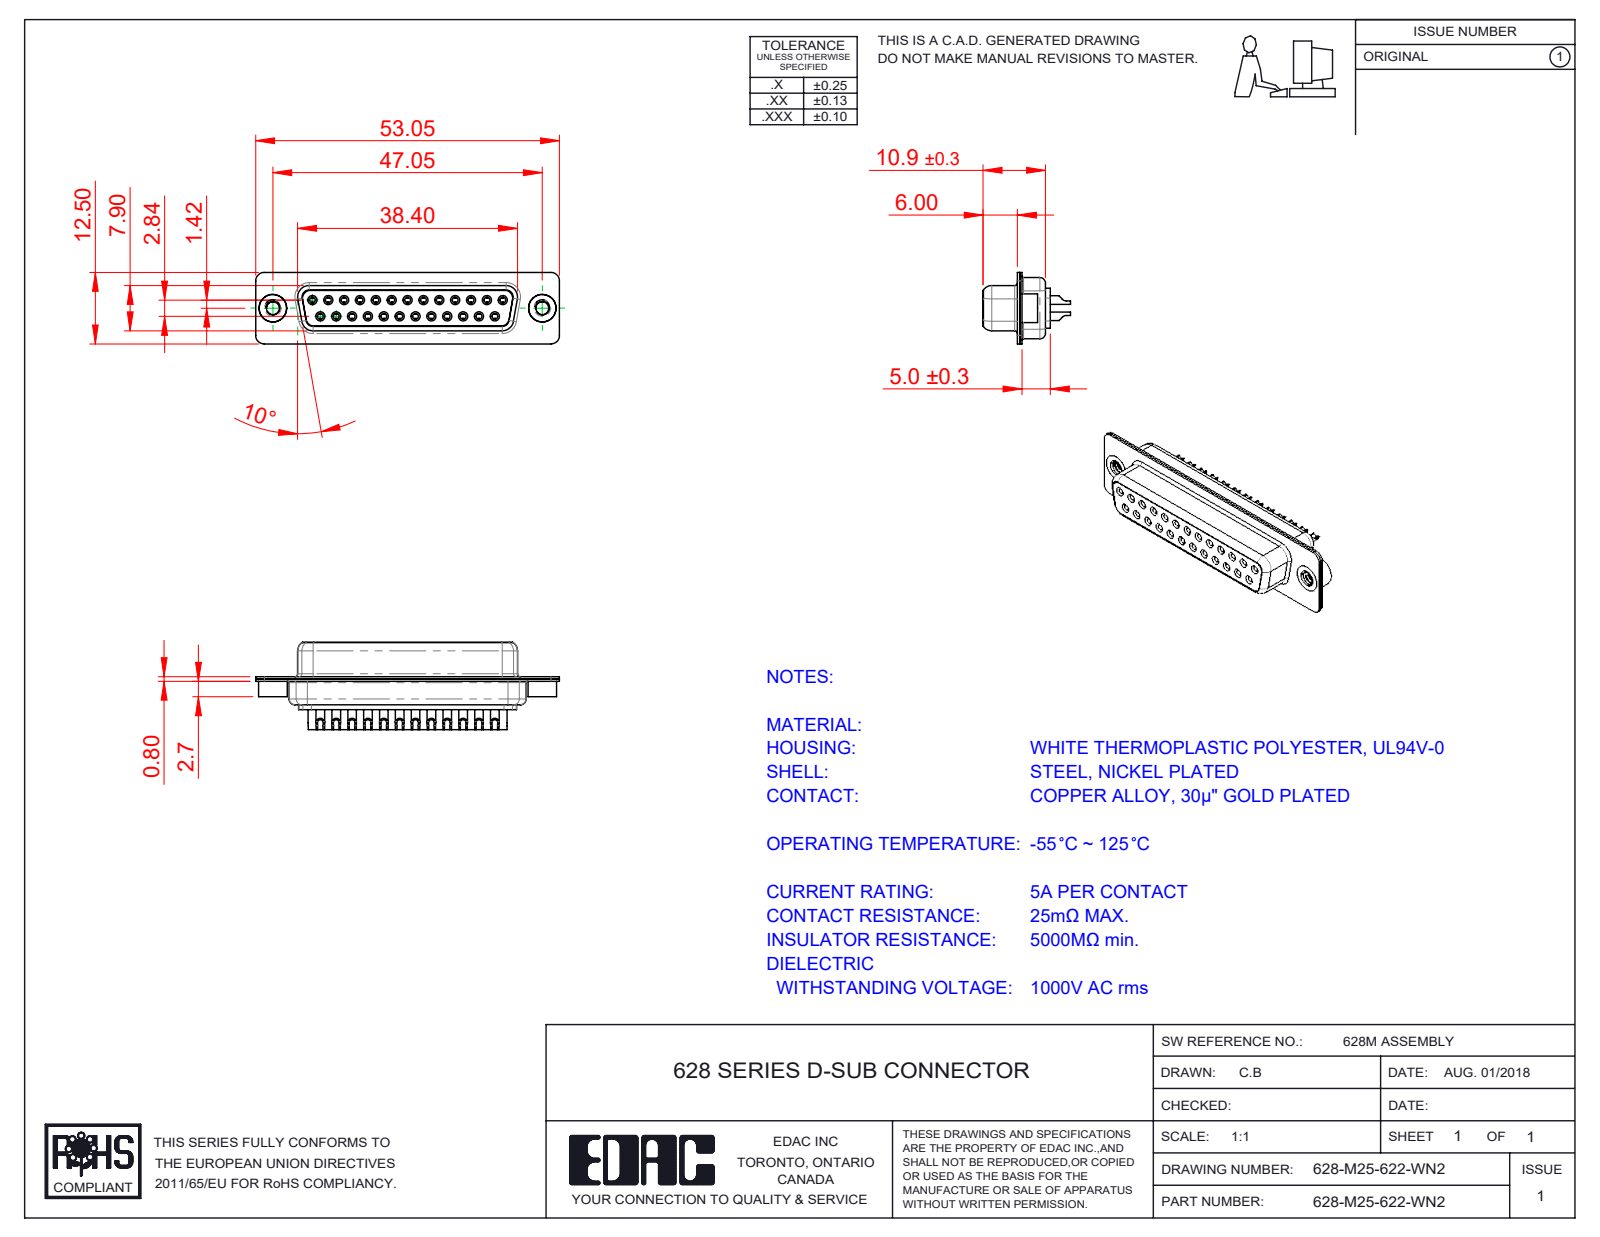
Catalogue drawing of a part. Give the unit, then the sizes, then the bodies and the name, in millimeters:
Units: millimetres
Overall size (bounding box): 53.05 × 15.25 × 12.5
Round holes (diameter × count): ⌀1 ×25, ⌀1.1 ×25, ⌀1.7 ×25, ⌀1.8 ×25, ⌀2 ×25, ⌀2.26 ×2, ⌀4 ×2, ⌀4.8 ×2
Round bosses / shafts (diameter × count): ⌀2.2 ×25, ⌀1.6 ×25, ⌀1.5 ×25, ⌀5 ×2, ⌀4.9 ×2
Partial cylindrical surfaces — rounded edges, fillets, slot ends (radius × count): R1.5 ×16, R2 ×12, R1.35 ×8, R1.6 ×8, R1 ×6, R0.25 ×4, R0.5 ×4, R0.6 ×4
Main face-to-face distances: 0.4, 1.4, 0.45, 8.45, 8.9, 1.8, 7.05, 0.85, 1, 1.85
Hole centre spacings: 3.16, 2.77, 5.54, 8.31, 11.08, 13.85, 5.04, 7.49
Volume: 3 776 mm³ · Surface area: 9 354 mm²
Bodies: 30 solids, 1655 faces (493 planar, 662 cylindrical, 500 other)
Part name (STEP PRODUCT): 628M Housing_25 Contacts; 628M Shell Front_25 Contacts; 628-M25-622-WN2; 628M Contact Row 2_22 (+3 more)
STEP written by: SolidWorks 2020 (CONFIG_CONTROL_DESIGN)
